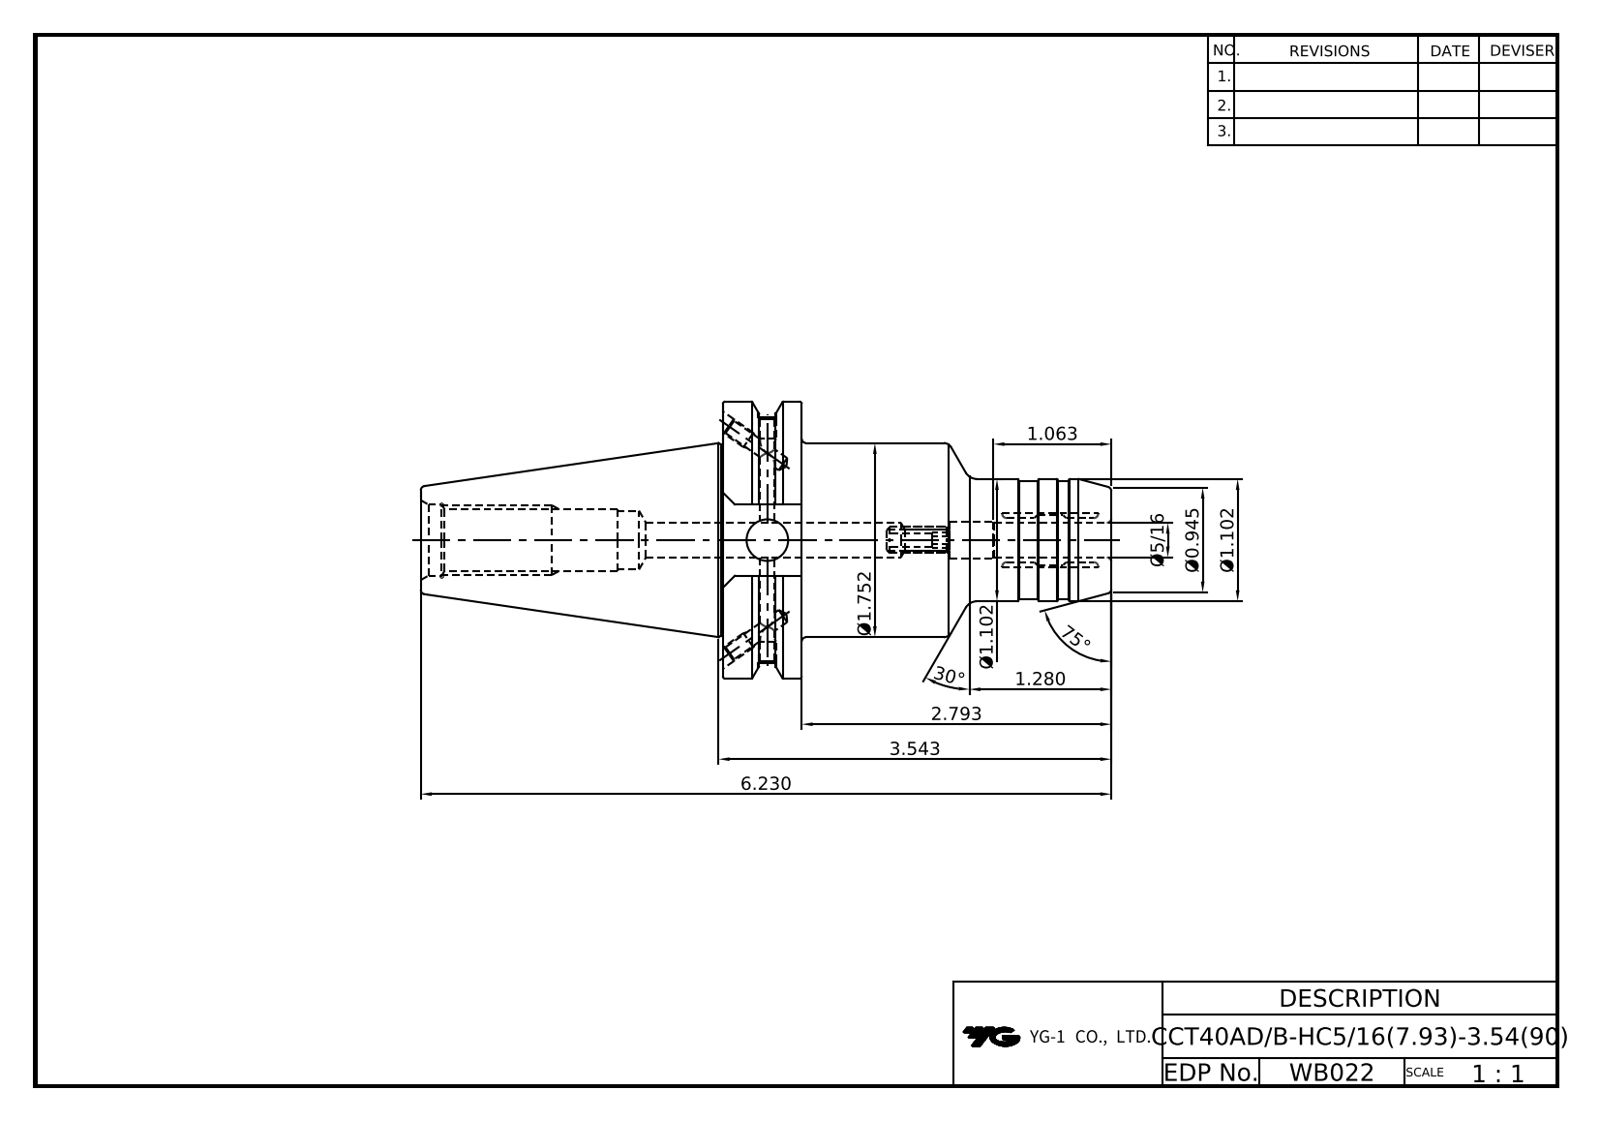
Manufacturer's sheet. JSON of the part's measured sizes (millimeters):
{"part_name": "LO-CCT40ADB-HC7.9375-90", "step_written_by": "Autodesk Inventor 2022 (AUTOMOTIVE_DESIGN)", "units": "millimeters", "bodies": {"solids": 1, "faces": 108, "planar": 34, "cylindrical": 35, "other": 39}, "overall_size": [158.25, 63.5, 61.09], "volume_mm3": 179995, "surface_area_mm2": 29743, "round_holes": [[3.24, 4], [4, 2], [4.2, 2], [4.92, 1], [7.94, 1], [8, 1], [9.5, 1], [9.53, 1], [13, 1], [13.39, 1], [16.3, 1]], "round_bosses_or_shafts": [[63.5, 1], [44.5, 1], [43.8, 1], [28, 1], [27, 1]], "partial_cylinders_radius": [[28.15, 1]], "face_to_face_distances": [18.05, 89, 70.95, 47.6, 16.38, 69.25, 87.3, 158.25, 81.34, 12.09]}
